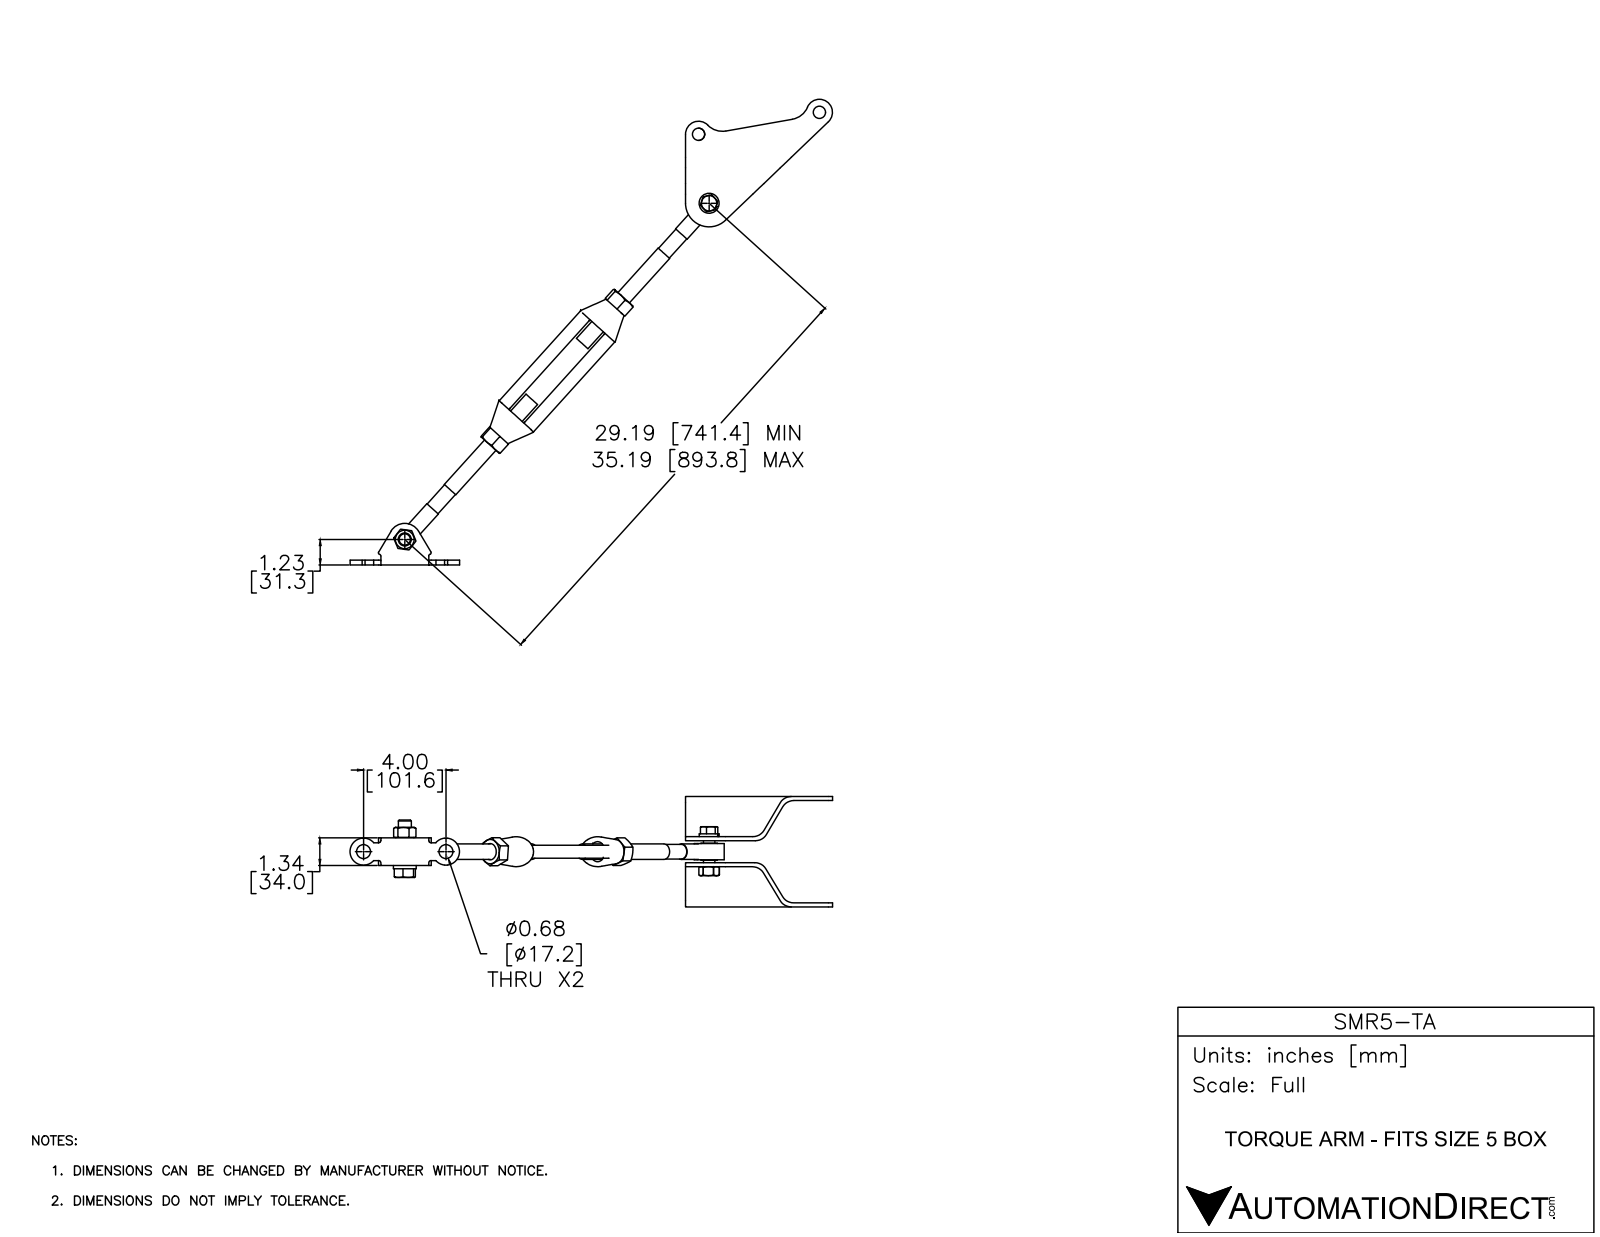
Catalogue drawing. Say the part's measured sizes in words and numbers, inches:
The part is named "SMR5-TA_4; SMR5-TA_1; SMR5-TA_5; SMR5-TARM (+2 more)". Its 3-D file was written by "SolidWorks 2017 (AUTOMOTIVE_DESIGN)". It is 15 solids with 334 faces: 131 planar, 122 cylindrical and 81 other. Overall it measures 23.397 by 22.574 by 5.354 inches. Its volume is 31.82 cubic inches and its surface area 281.3 square inches. Round holes: 4 of diameter 0.591, 2 of diameter 0.677, 2 of diameter 0.689, 2 of diameter 0.787, 1 of diameter 0.551, 1 of diameter 0.559, 1 of diameter 0.571, 1 of diameter 0.63, 1 of diameter 0.638, 1 of diameter 0.646, 1 of diameter 0.65, 1 of diameter 0.795. Round bosses or shafts: 4 of diameter 0.75, 2 of diameter 1.457, 2 of diameter 0.711, 2 of diameter 0.63, 1 of diameter 1.102, 1 of diameter 0.965, 1 of diameter 0.878, 1 of diameter 0.787. Partial cylindrical surfaces (rounded edges, fillets, slot ends): 8 of radius 0.591, 4 of radius 0.079, 4 of radius 0.118, 2 of radius 0.197, 2 of radius 0.63, 2 of radius 0.654, 2 of radius 0.984, 1 of radius 0.5. The main face-to-face distances are 0.197, 5.157, 1.949, 3.209, 0.138, 0.236, 5.354, 4.961, 1.26, 1.063. The hole center spacings are 3.385, 3.385, 4, 5.959, 5.962, 6.936, 21.992, 24.272.
